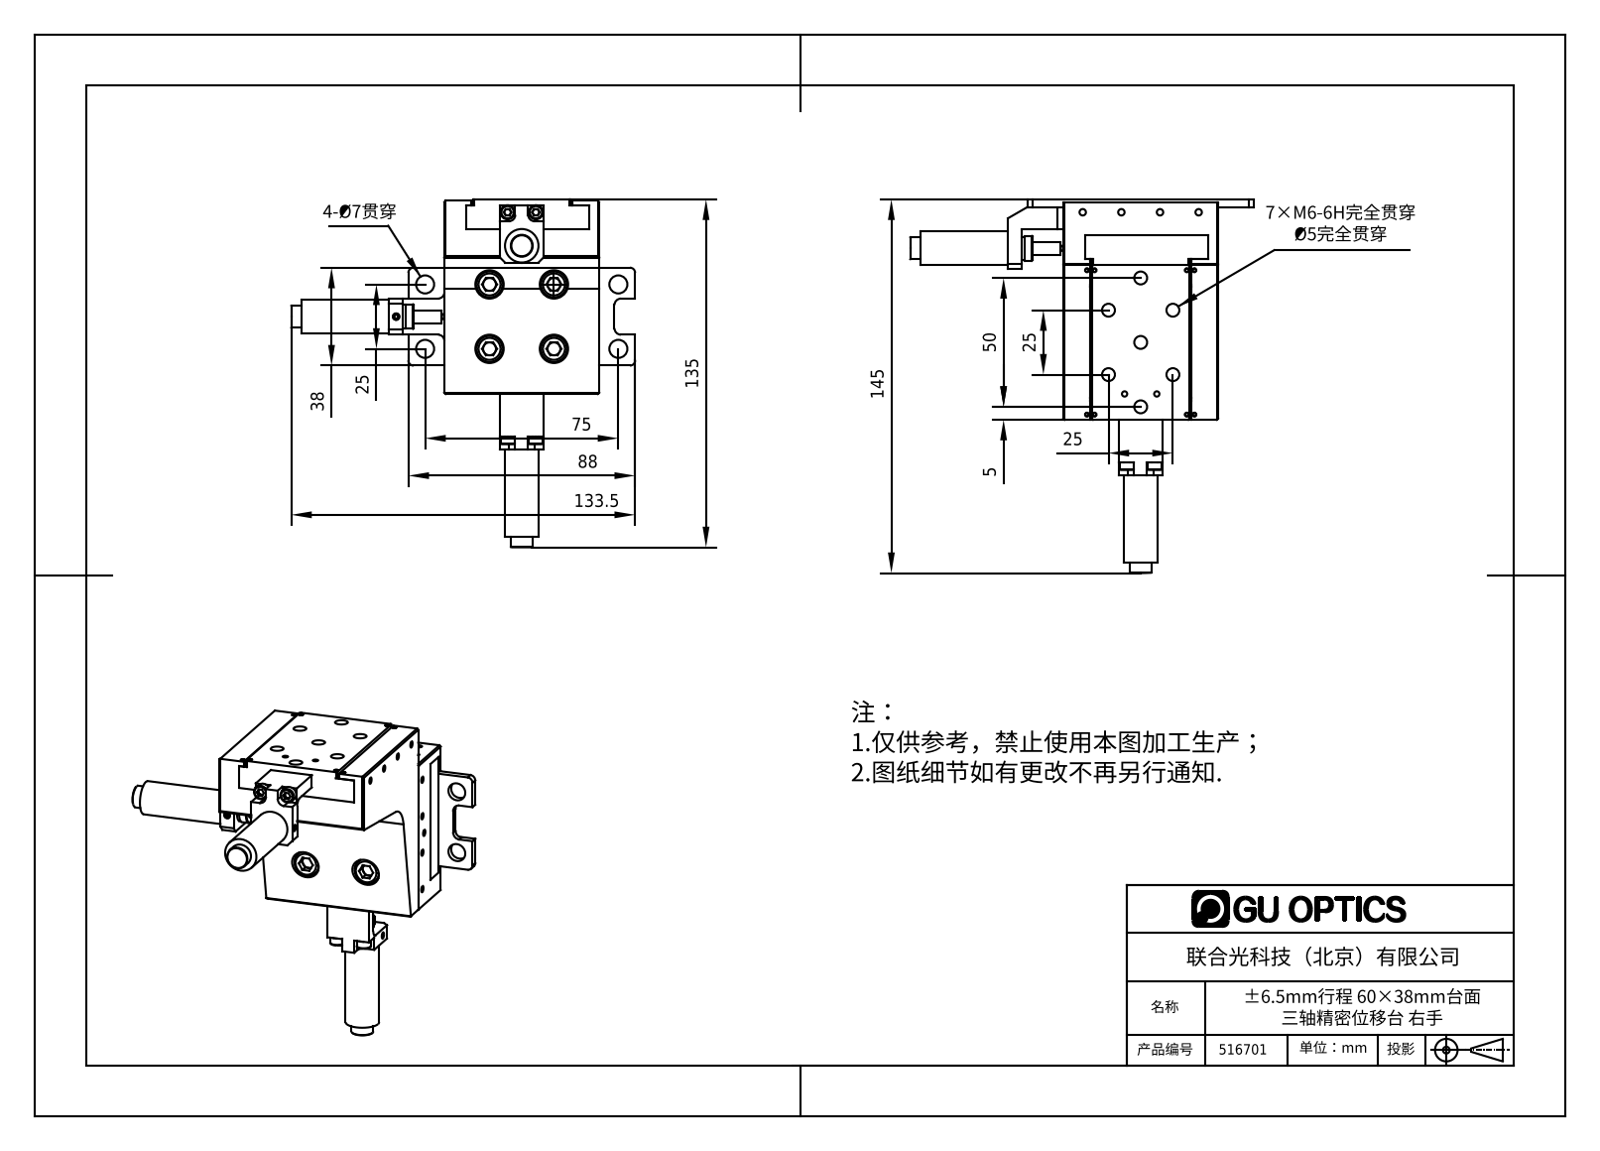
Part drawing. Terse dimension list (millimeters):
name: 516701
written by: SolidWorks 2016 (AUTOMOTIVE_DESIGN)
unit: mm
bodies: 69 solids, 920 faces (424 planar, 344 cylindrical, 152 other)
size: 145 × 135 × 133.5
volume: 242 558 mm³; area: 82 080 mm²
holes: 20× ⌀2.5, 17× ⌀1.5, 16× ⌀2.05, 16× ⌀5, 4× ⌀3.5, 4× ⌀6.5, 4× ⌀7, 4× ⌀11
bosses: 7× ⌀1.5, 5× ⌀3, 4× ⌀10, 4× ⌀6, 4× ⌀5.5, 4× ⌀2.5, 3× ⌀13, 3× ⌀9.5
rounds: 10× R2.5, 4× R2, 3× R0.75, 1× R10
face distances: 2, 11.5, 11, 13.5, 60, 4, 9, 0.5, 2.5, 13
hole spacings: 17.61, 25, 13.98, 22.53, 36.78, 41.35, 52.46, 14.91
